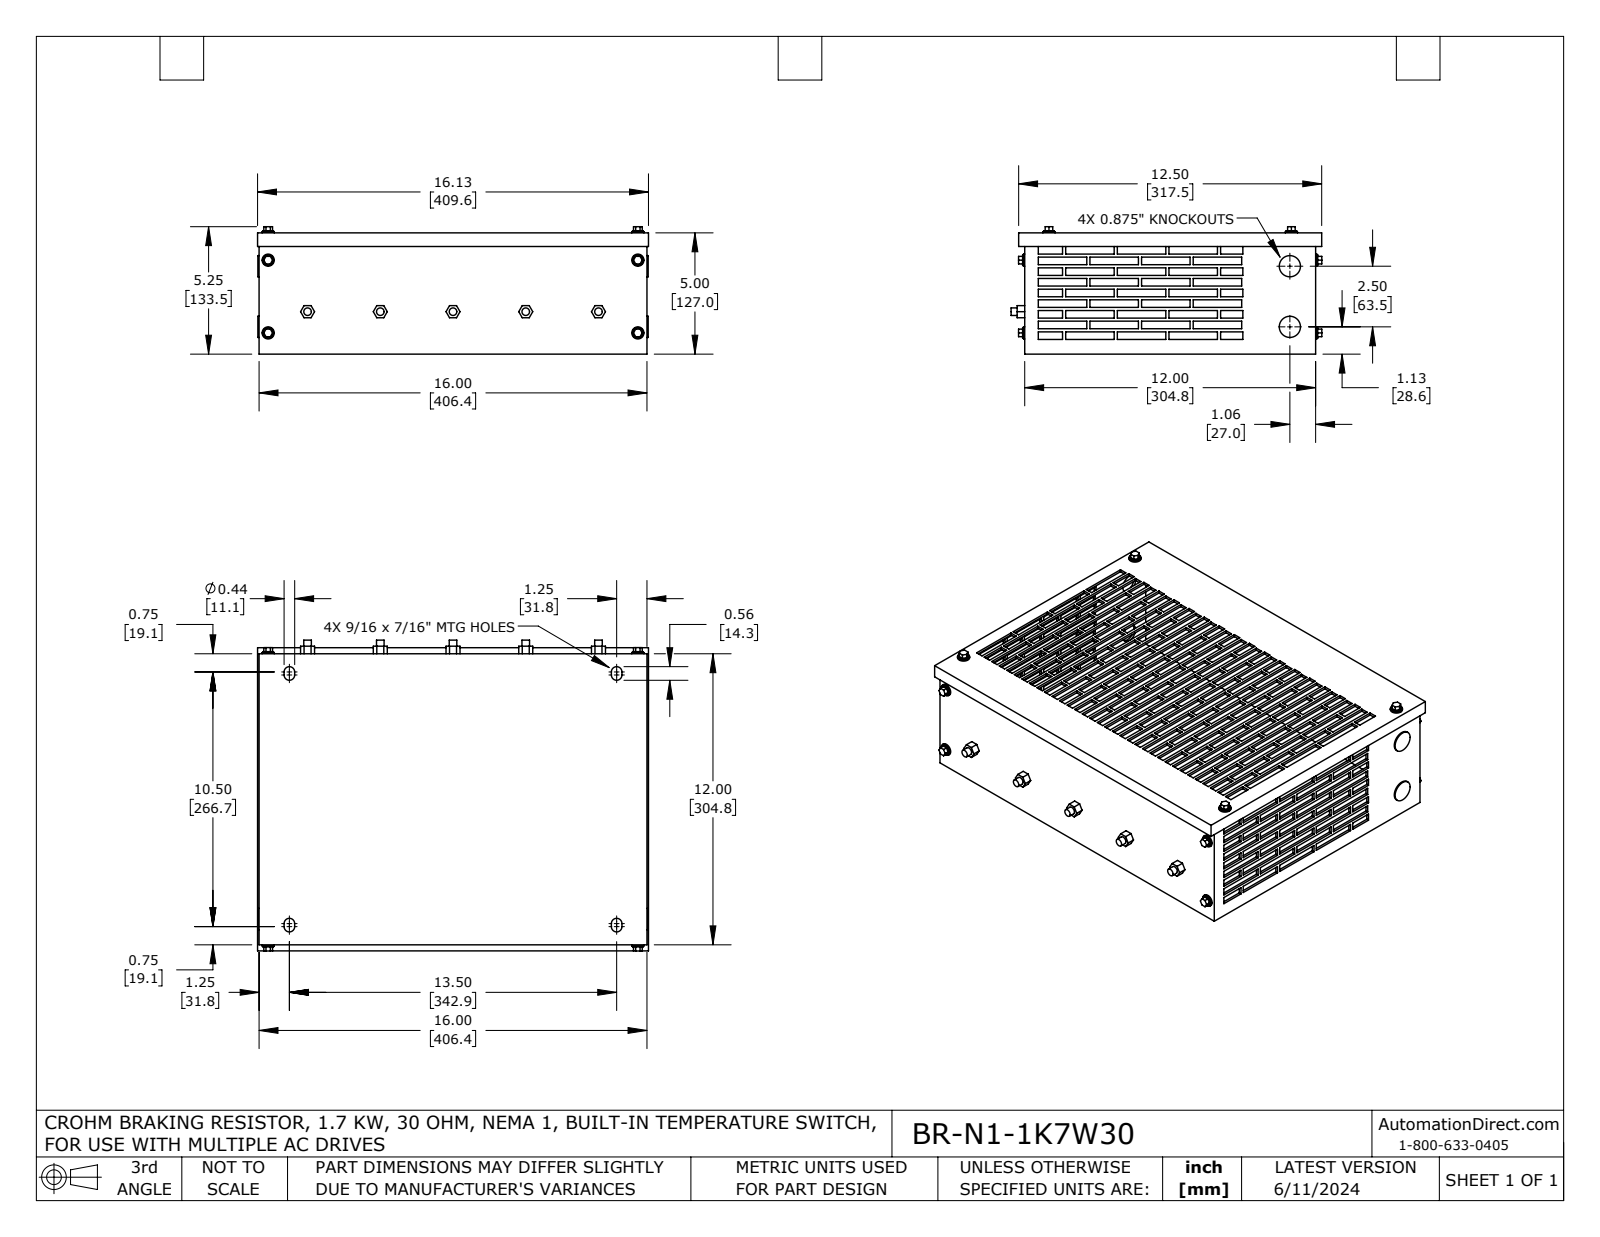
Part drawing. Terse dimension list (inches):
name: BR-N1-1K7W30
written by: SolidWorks 2021 (AUTOMOTIVE_DESIGN)
unit: in
bodies: 34 solids, 1255 faces (1149 planar, 106 cylindrical, 0 other)
size: 16.125 × 12.817 × 5.254
volume: 54.77 in³; area: 1 200 in²
holes: 8× ⌀0.25, 2× ⌀0.75
bosses: 8× ⌀0.5, 8× ⌀0.437, 5× ⌀0.313, 2× ⌀0.875
rounds: 8× R0.219
face distances: 0.1, 4.9, 11.9, 5, 4.8, 12, 11.8, 15.9, 16, 0.25
hole spacings: 15.25, 3, 10, 15.543, 18.237, 2.5
